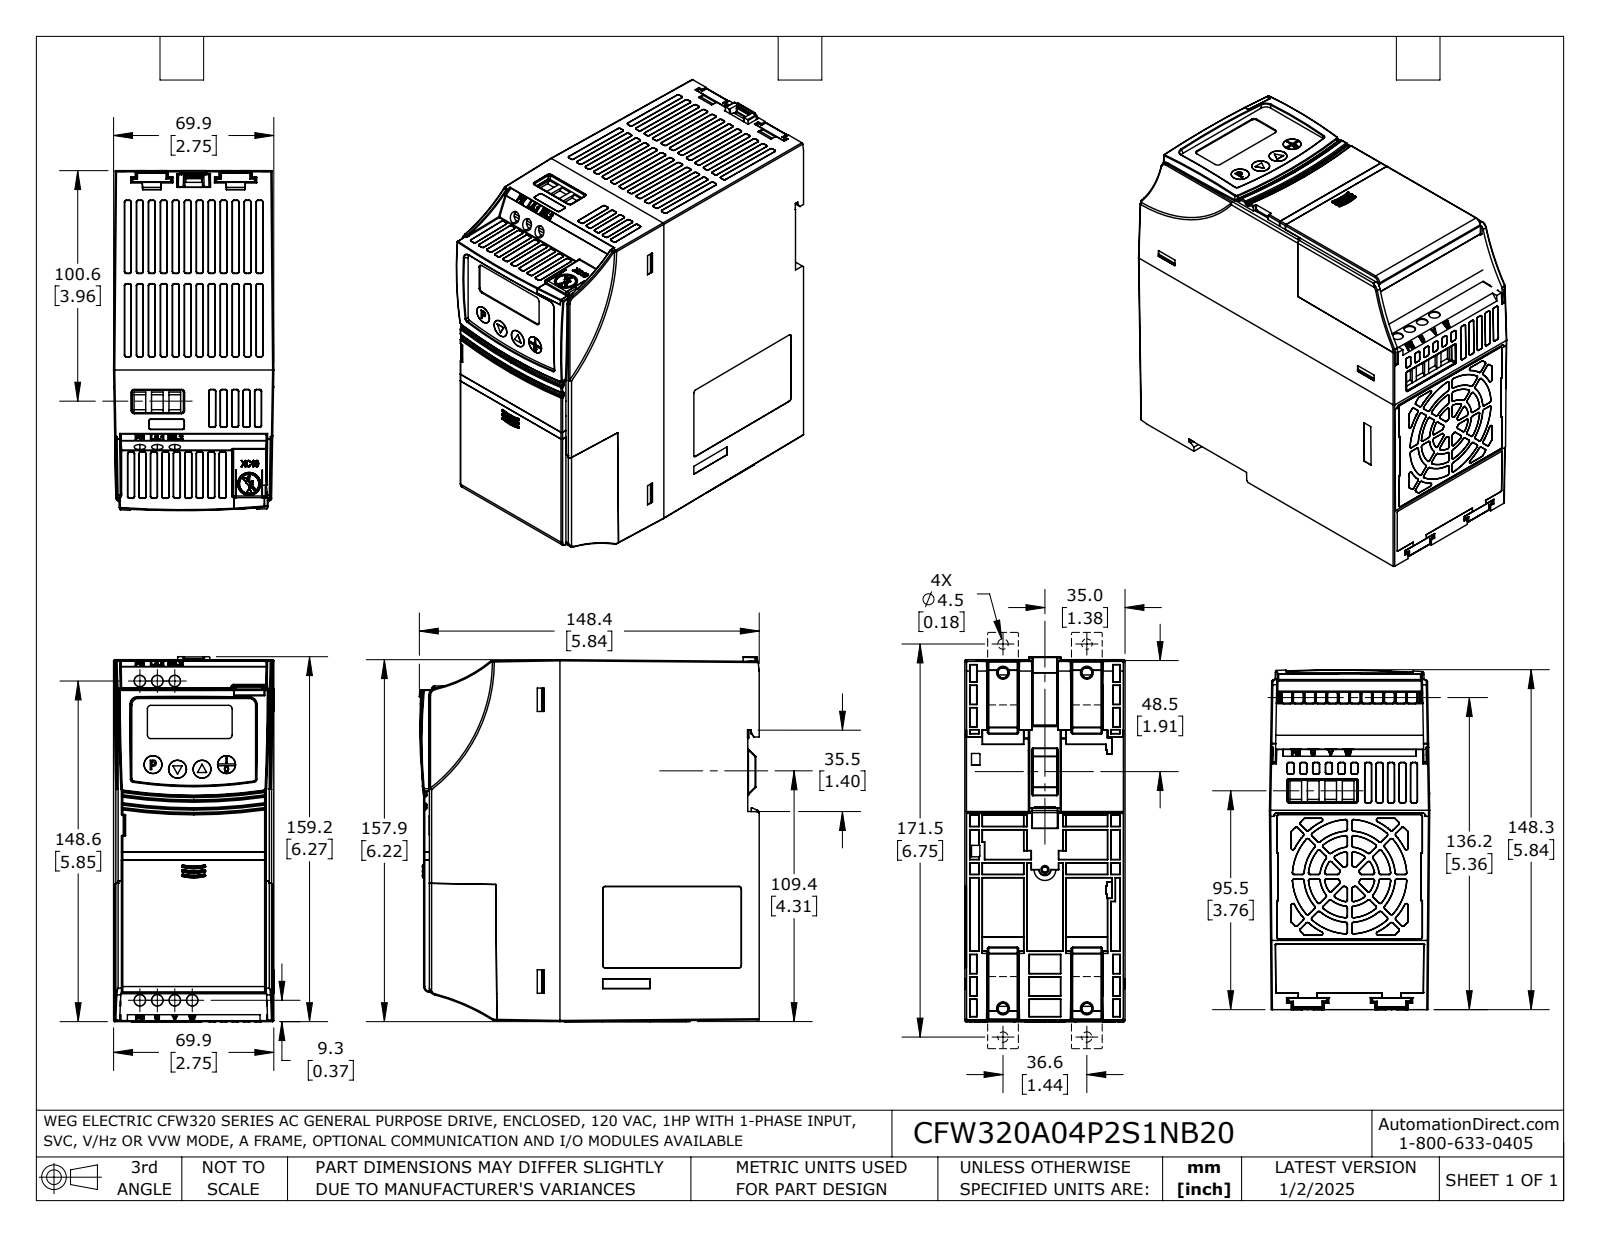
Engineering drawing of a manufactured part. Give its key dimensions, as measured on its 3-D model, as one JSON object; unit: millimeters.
{"part_name": "CFW320A04P2S1NB20", "step_written_by": "SolidWorks 2021 (AUTOMOTIVE_DESIGN)", "units": "millimeters", "bodies": {"solids": 6, "faces": 3715, "planar": 1587, "cylindrical": 853, "other": 1275}, "overall_size": [159.2, 148.4, 70], "volume_mm3": 249700, "surface_area_mm2": 199400, "round_holes": [[5, 3]], "partial_cylinders_radius": [[0.3, 327], [0.5, 150], [1, 13], [0.8, 5], [3, 3], [0.3, 2], [2.5, 1], [3.2, 1]], "face_to_face_distances": [1.8, 1.4, 0.5, 1.3, 152.4, 135.4, 134, 141.5, 140.1, 6.1], "hole_center_spacings": [7.6, 15.2]}
